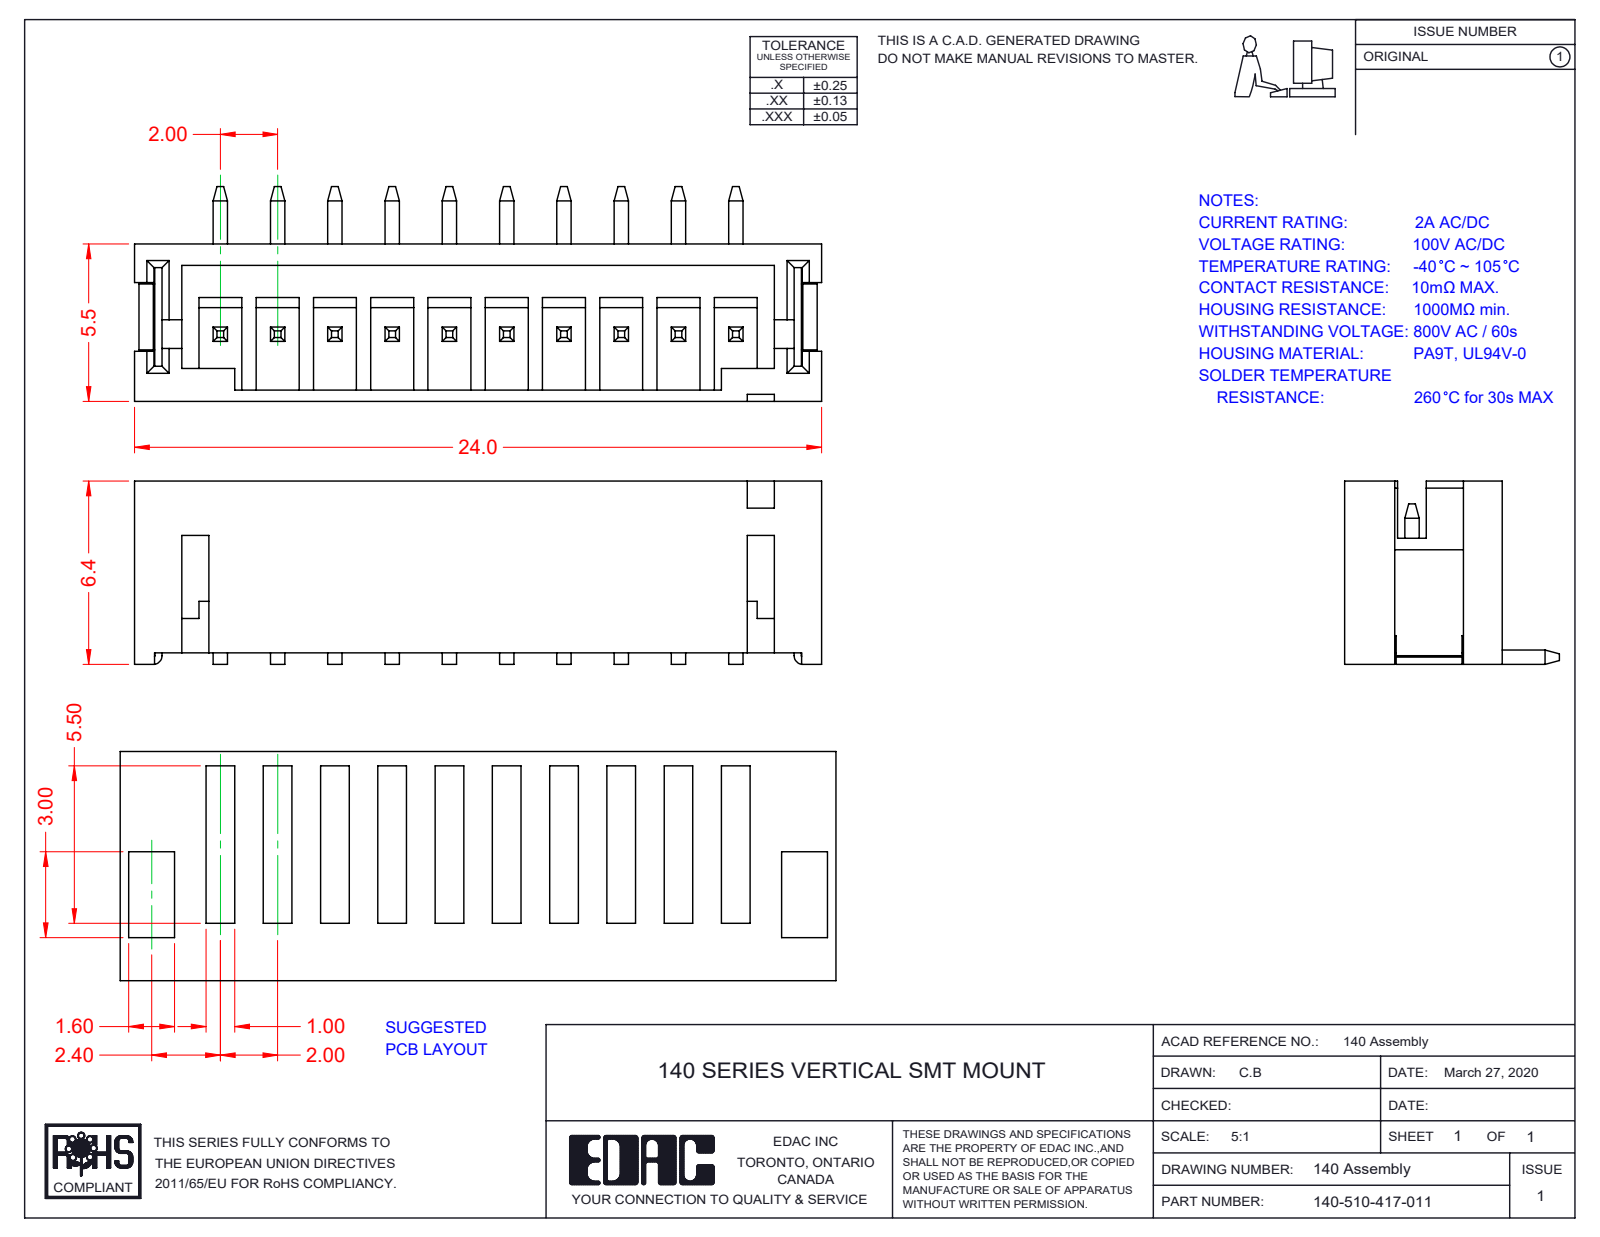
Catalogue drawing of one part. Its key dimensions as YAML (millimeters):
part_name: "140-510-417-011; V SMT Contact; V SMT Housing_510; V SMT Pad"
step_written_by: "SolidWorks 2016 (CONFIG_CONTROL_DESIGN)"
units: millimeters
bodies: {solids: 13, faces: 480, planar: 456, cylindrical: 24, other: 0}
overall_size: [24, 7.5, 6.4]
volume: 351
surface_area: 1269
partial_cylinders:
  - {radius: 0.3, count: 2}
  - {radius: 0.55, count: 1}
face_to_face_distances: [5.5, 0.75, 4.75, 0.4, 0.5, 4.35, 5.1, 0.6, 0.55, 2.2]
